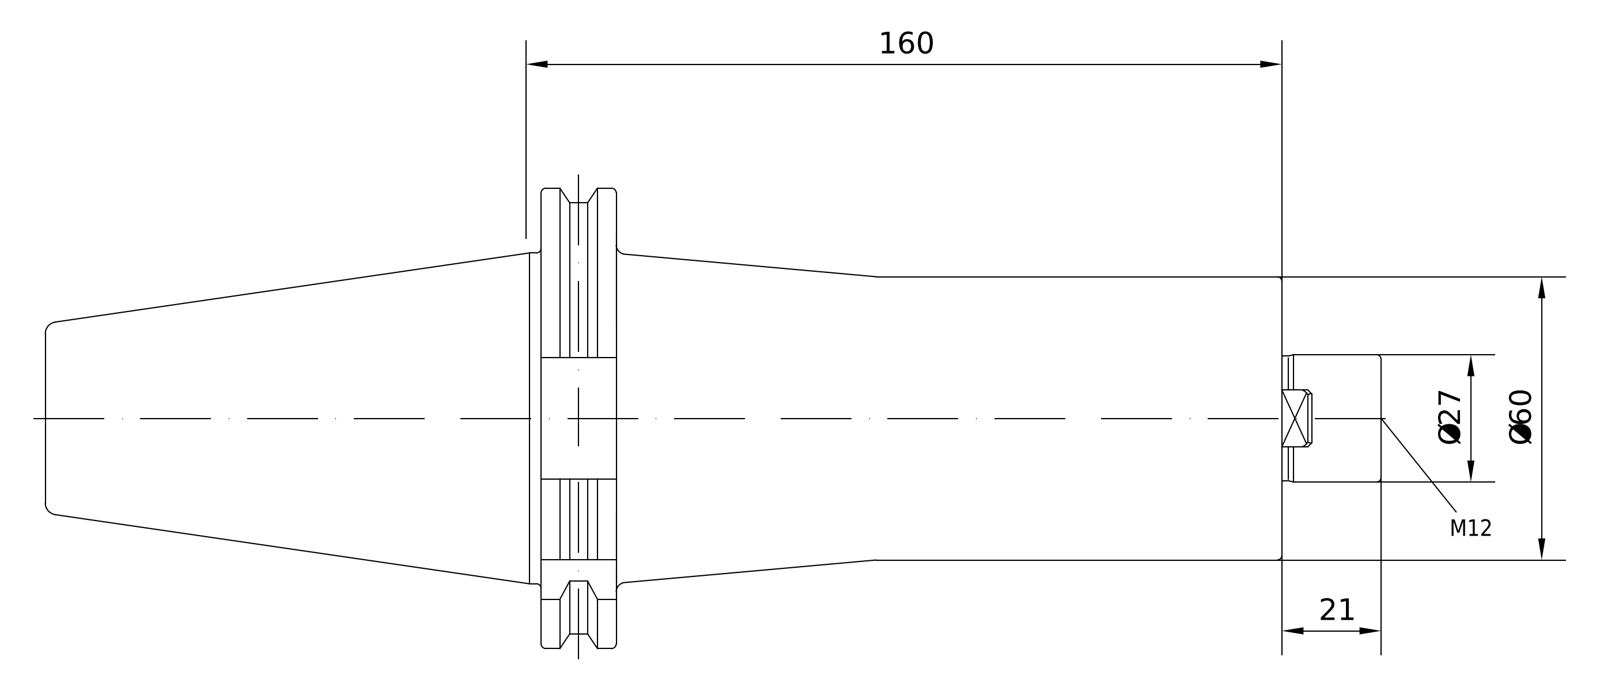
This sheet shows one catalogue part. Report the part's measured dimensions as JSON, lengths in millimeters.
{"part_name": "50-352-27", "step_written_by": "PRO/ENGINEER BY PARAMETRIC TECHNOLOGY CORPORATION, 2010430 (CONFIG_CONTROL_DESIGN)", "units": "millimeters", "bodies": {"solids": 1, "faces": 112, "planar": 32, "cylindrical": 28, "other": 52}, "overall_size": [282.6, 97.47, 94], "volume_mm3": 767301, "surface_area_mm2": 73086, "round_holes": [[10.2, 1], [12, 1], [20.75, 1], [25.01, 1], [25.7, 1]], "round_bosses_or_shafts": [[91, 1], [69.15, 1], [60, 1], [27, 1], [24.01, 1]], "partial_cylinders_radius": [[1.75, 1], [48.74, 1]], "face_to_face_distances": [15.85, 156.8, 140.95, 177.8, 161.95, 21, 72.8, 104.8, 120.65, 261.6]}
